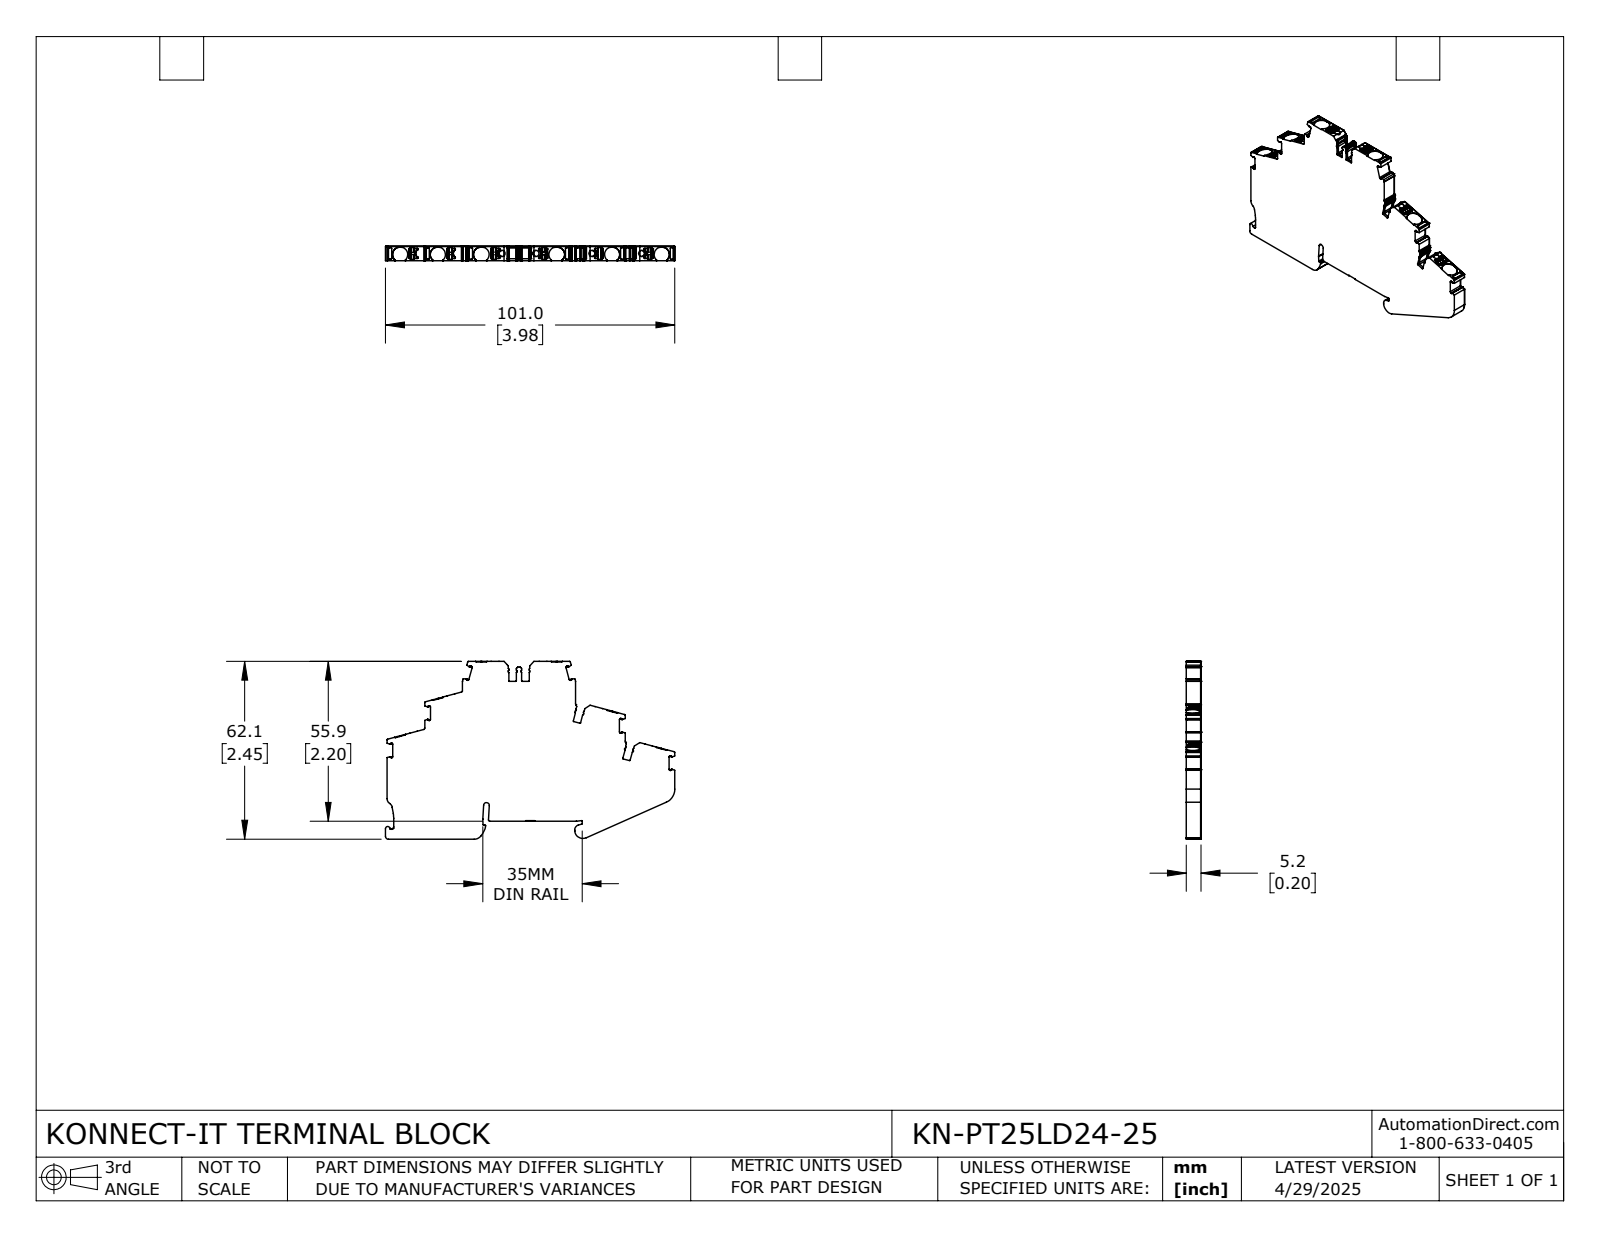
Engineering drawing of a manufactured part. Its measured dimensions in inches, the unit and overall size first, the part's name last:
Units: inches
Overall size (bounding box): 3.977 × 2.445 × 0.203
Round holes (diameter × count): ⌀0.083 ×4
Partial cylindrical surfaces — rounded edges, fillets, slot ends (radius × count): R0.008 ×128, R0.004 ×49, R0.012 ×47, R0.02 ×26, R0.006 ×24, R0.016 ×17, R0.024 ×14, R0.006 ×12
Main face-to-face distances: 0.203, 0.246, 0.079, 2.191, 2.437, 0.319, 0.682, 0.519, 2.445, 2.199
Hole centre spacings: 0.466, 0.792
Volume: 1.354 in³ · Surface area: 16.76 in²
Bodies: 1 solid, 1212 faces (579 planar, 528 cylindrical, 105 other)
Part name (STEP PRODUCT): KN-PT25LD24-25
STEP written by: SolidWorks 2024 (CONFIG_CONTROL_DESIGN)
